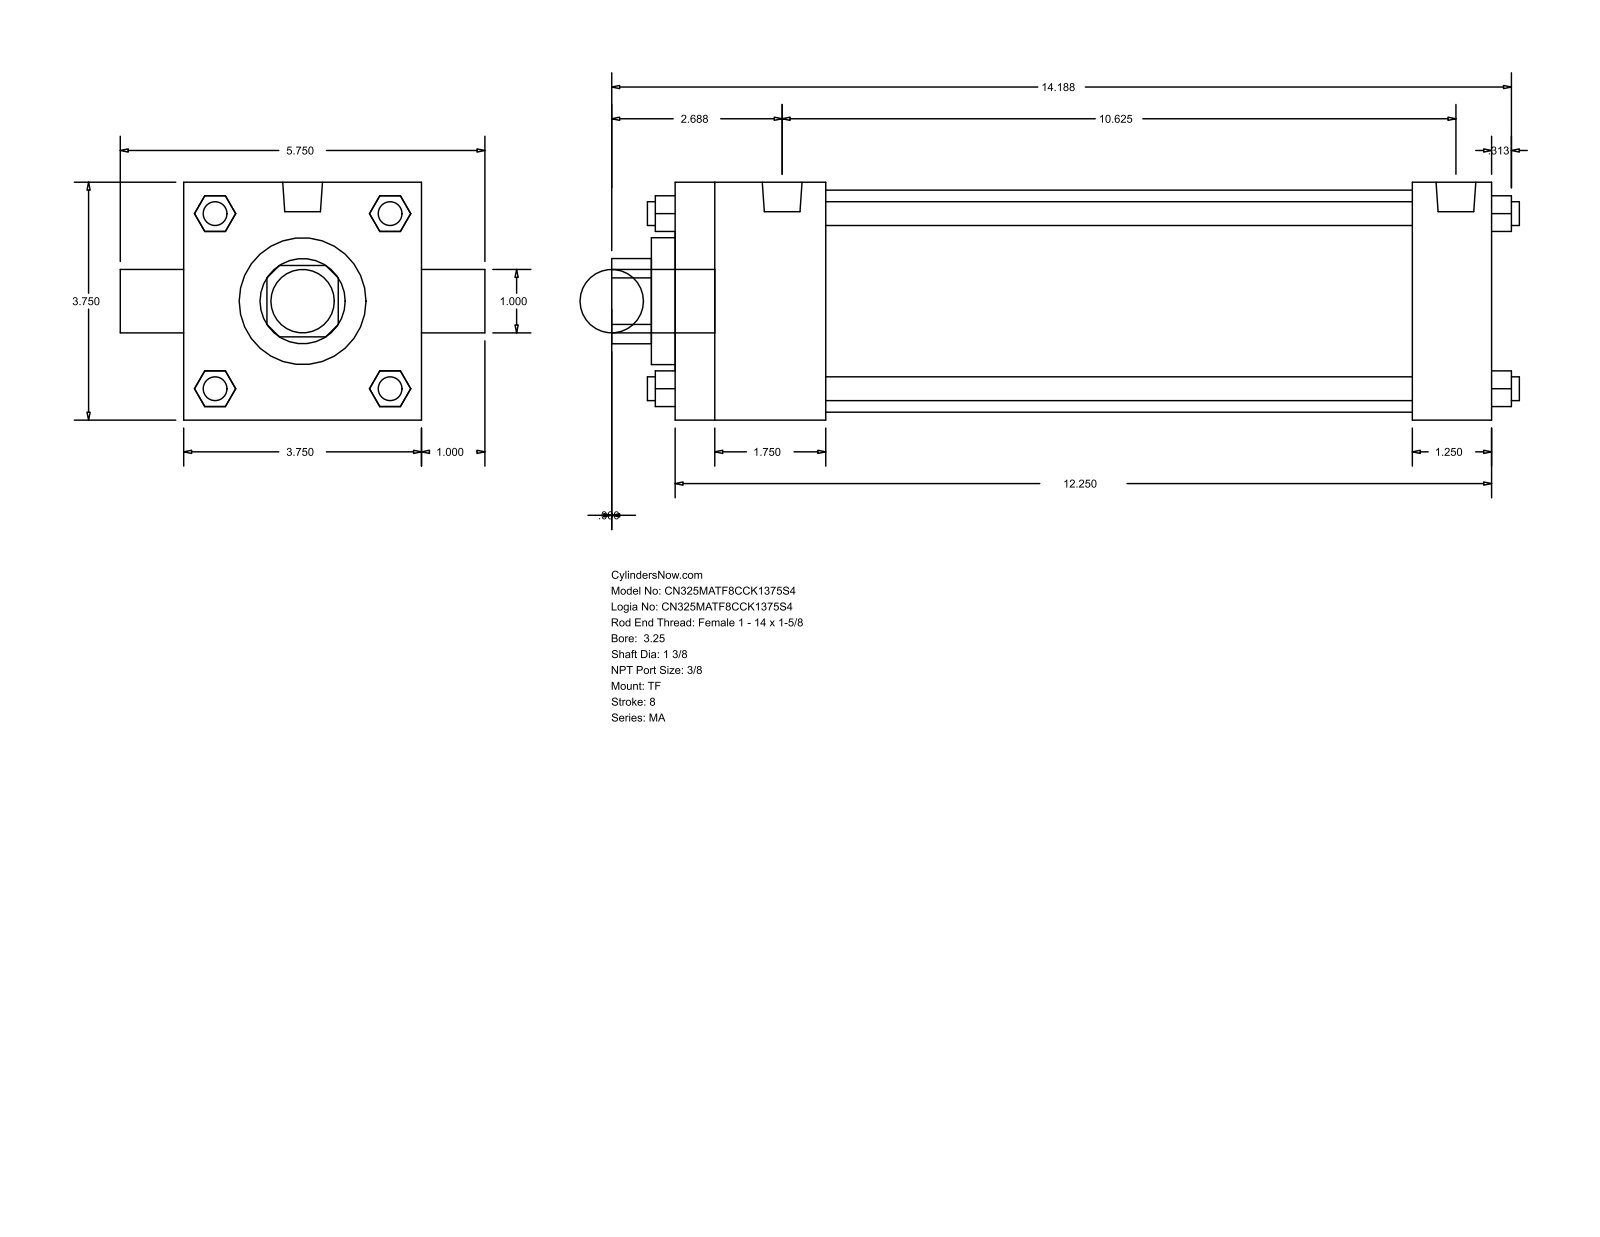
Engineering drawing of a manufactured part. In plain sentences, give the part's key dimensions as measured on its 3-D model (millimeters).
The part is named "MA_TF__0325_1.375". Its 3-D file was written by "GSSL Pune (CONFIG_CONTROL_DESIGN)". It is 0 solids with 120 faces: 92 planar, 28 cylindrical and 0 other. Overall it measures 363.54 by 146.05 by 95.25 millimeters. Round holes: 1 of diameter 25.4, 1 of diameter 34.92, 1 of diameter 50.8, 1 of diameter 88.9. Round bosses or shafts: 4 of diameter 9.53, 3 of diameter 11.11, 2 of diameter 15.93, 1 of diameter 25.4. Partial cylindrical surfaces (rounded edges, fillets, slot ends): 1 of radius 17.06. The main face-to-face distances are 95.24, 327.03, 60.32, 295.28, 234.96, 266.71, 31.75, 9.52, 69.84, 304.8.
